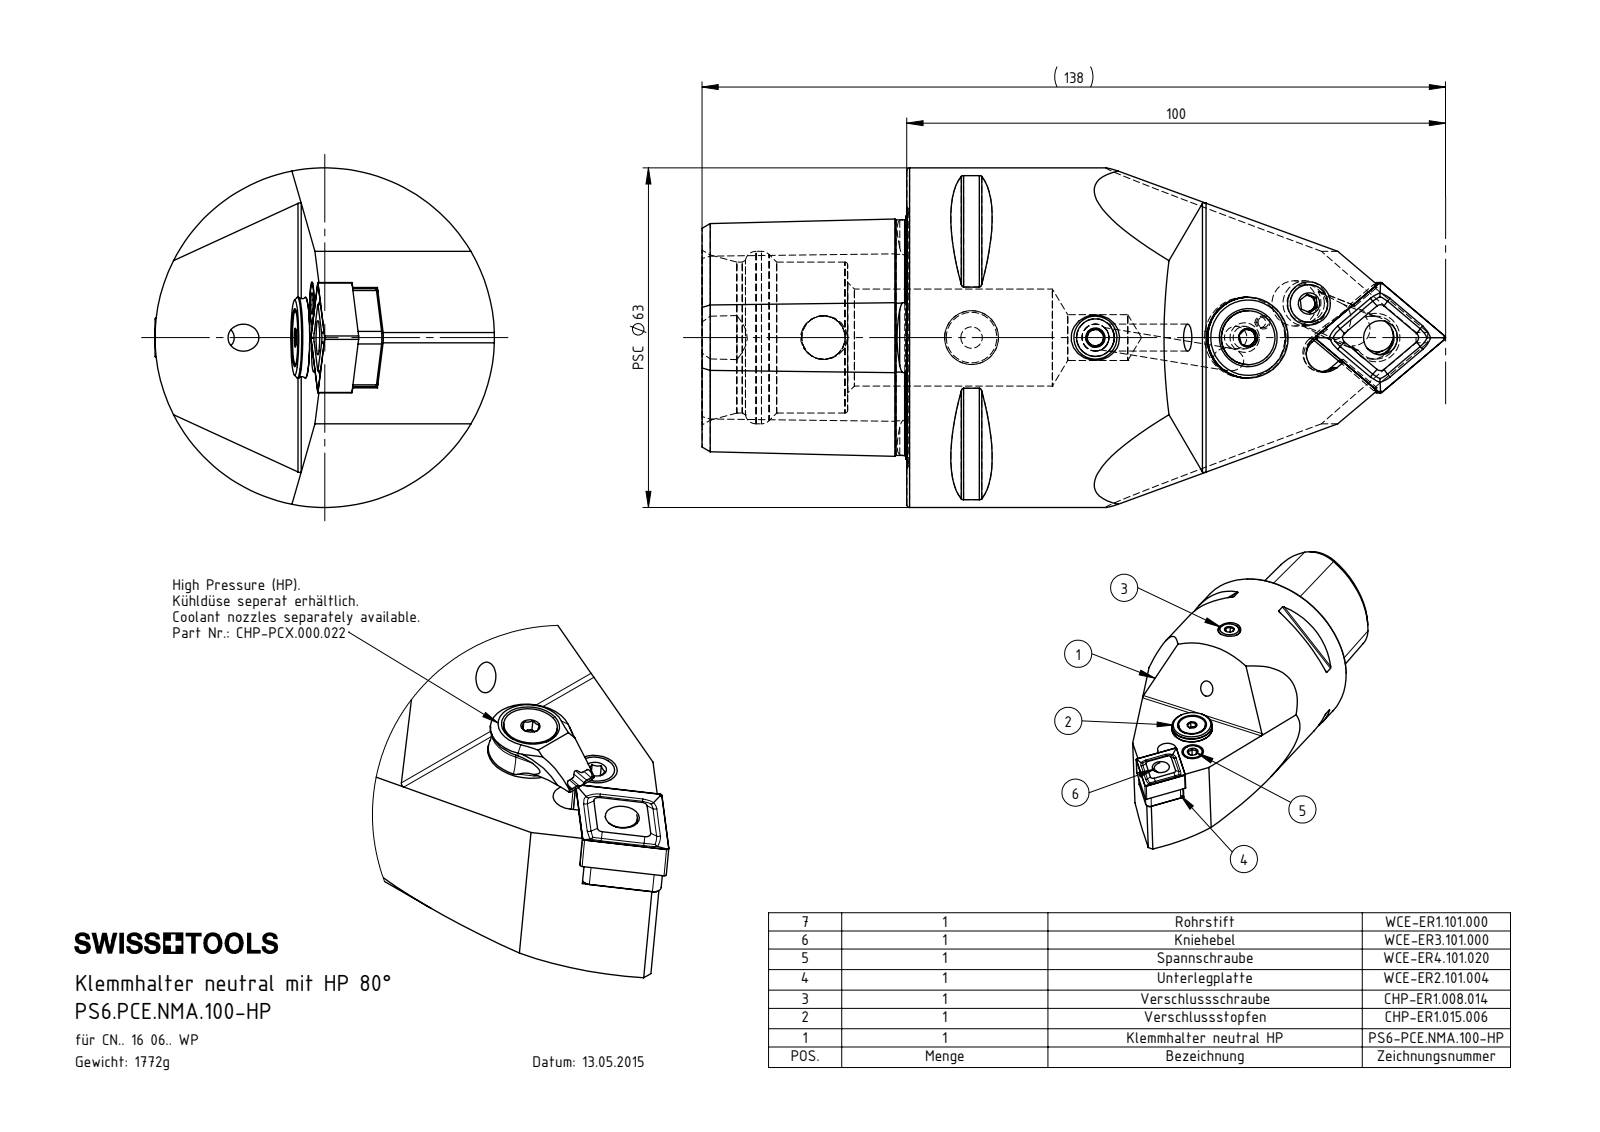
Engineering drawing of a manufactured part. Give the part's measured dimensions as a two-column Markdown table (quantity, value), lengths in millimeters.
| quantity | value |
| --- | --- |
| part name | PS6.PCE.NMA.100-HP; WCE-ER2.101.004_A; ISO 8752 2x8; WCE-ER4.101.020_A (+8 more) |
| STEP written by | SolidWorks 2022 (CONFIG_CONTROL_DESIGN) |
| units | millimeters |
| bodies | 12 solids, 545 faces (147 planar, 145 cylindrical, 253 other) |
| overall size | 138 × 63 × 63 |
| volume | 225 058 mm³ |
| surface area | 39 205 mm² |
| round holes (diameter × count) | 4.2 × 2, 5 × 2, 7 × 2, 1.2 × 1, 2 × 1, 3 × 1, 5.3 × 1, 6.35 × 1, 7.9 × 1, 8.1 × 1, 8.4 × 1, 8.5 × 1 |
| round bosses / shafts (diameter × count) | 8 × 2, 63 × 1, 14.85 × 1, 13.4 × 1, 10 × 1, 7.9 × 1, 6.4 × 1, 6 × 1 |
| partial cylindrical surfaces (radius × count) | 1 × 11, 0.5 × 10, 0.4 × 4, 6 × 4, 0.3 × 3, 3.5 × 3, 1.1 × 2, 1.2 × 2 |
| main face-to-face distances | 15.07, 38, 0.8, 6.04, 10.8, 24.88, 11, 27, 4.76, 15.87 |
| hole center spacings | 4.5, 4.52, 13.18, 24.88, 25.13, 8.76, 8.79, 14.76 |
